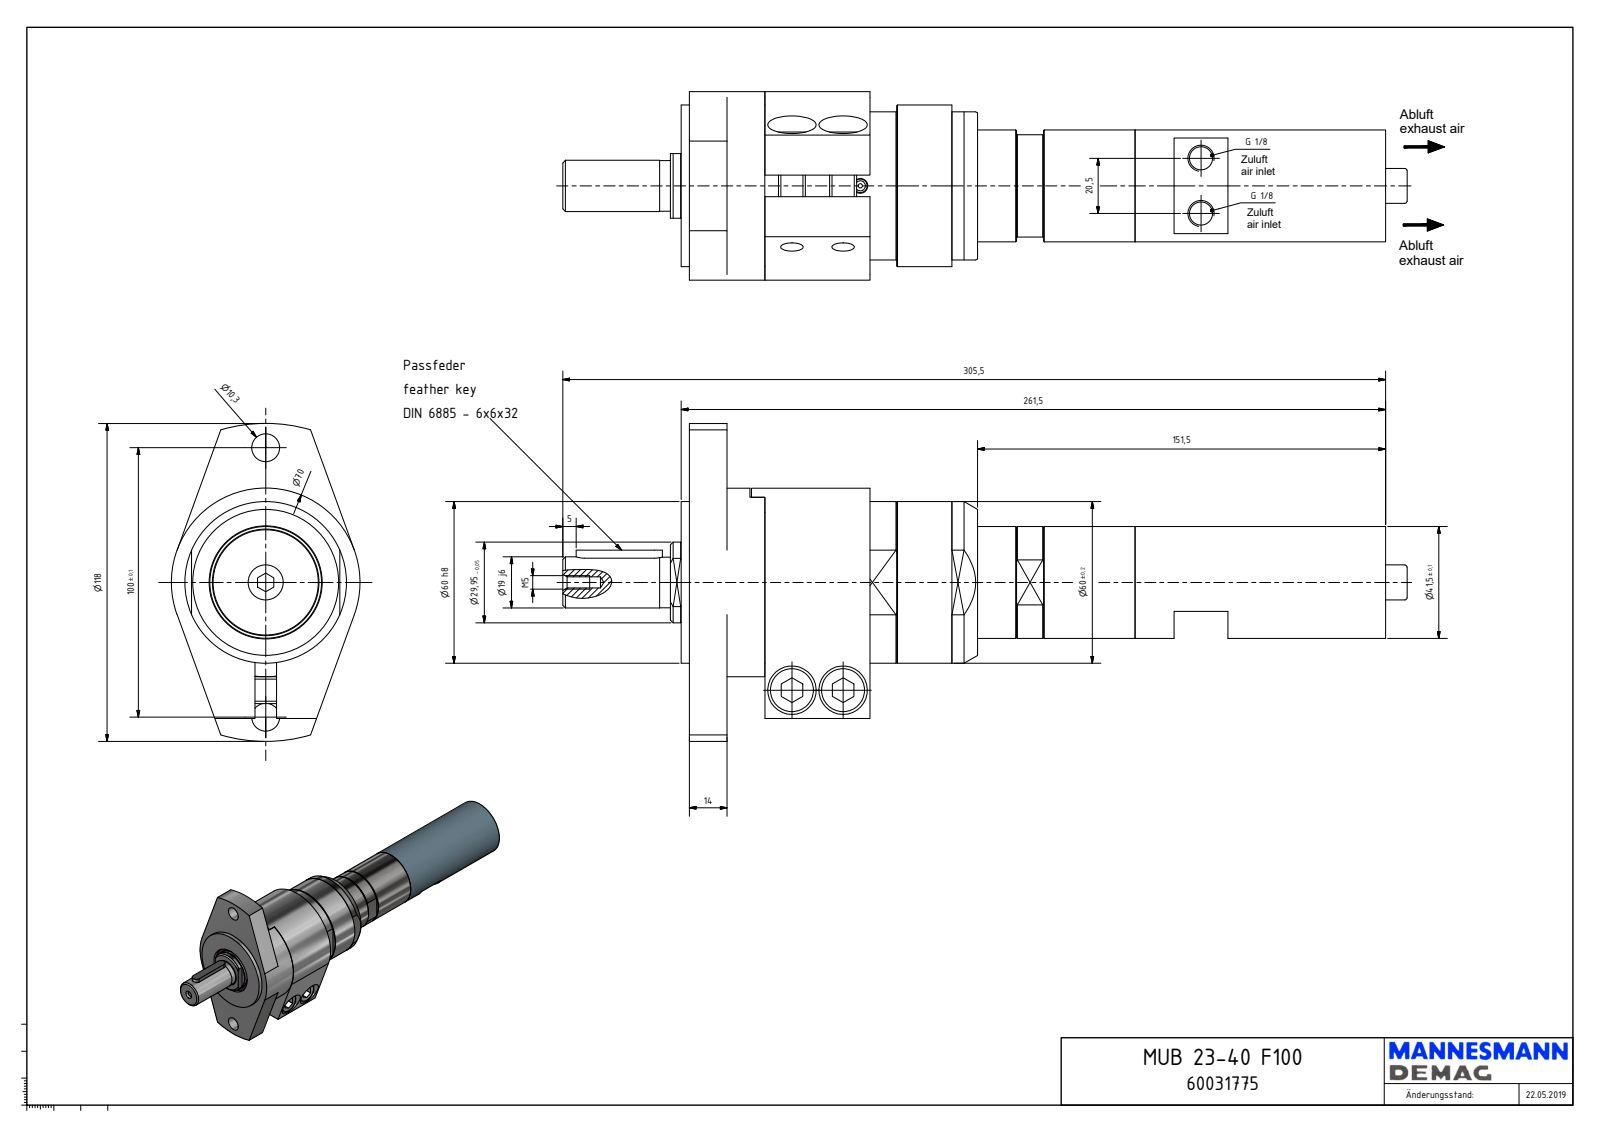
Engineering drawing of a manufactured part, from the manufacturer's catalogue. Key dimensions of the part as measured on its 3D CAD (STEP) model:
Part name (STEP PRODUCT): MUB 23-40 F100_60031775
STEP written by: Autodesk Inventor 2018 (AUTOMOTIVE_DESIGN)
Units: millimetres
Bodies: 1 solid, 254 faces (124 planar, 83 cylindrical, 47 other)
Overall size (bounding box): 313.5 × 118 × 70
Volume: 642 000 mm³ · Surface area: 80 691 mm²
Round holes (diameter × count): ⌀2 ×2, ⌀8.38 ×2, ⌀8.57 ×2, ⌀10.3 ×2, ⌀10.5 ×2, ⌀18 ×2, ⌀1.55 ×1, ⌀4 ×1, ⌀4.13 ×1, ⌀5.5 ×1, ⌀8.5 ×1, ⌀13 ×1
Round bosses / shafts (diameter × count): ⌀16 ×2, ⌀10 ×2, ⌀70 ×1, ⌀60 ×1, ⌀55.18 ×1, ⌀41.5 ×1, ⌀39 ×1, ⌀38.64 ×1
Partial cylindrical surfaces — rounded edges, fillets, slot ends (radius × count): R1.6 ×2, R2 ×2, R2.5 ×2, R3 ×2, R4.5 ×1, R8 ×1, R8.1 ×1, R11.56 ×1
Main face-to-face distances: 14, 17, 3, 70.1, 39, 67.1, 53.1, 31.1, 28.1, 14.1
Hole centre spacings: 12.94, 48.3, 50, 54.79, 126.91, 19, 20.5, 25
